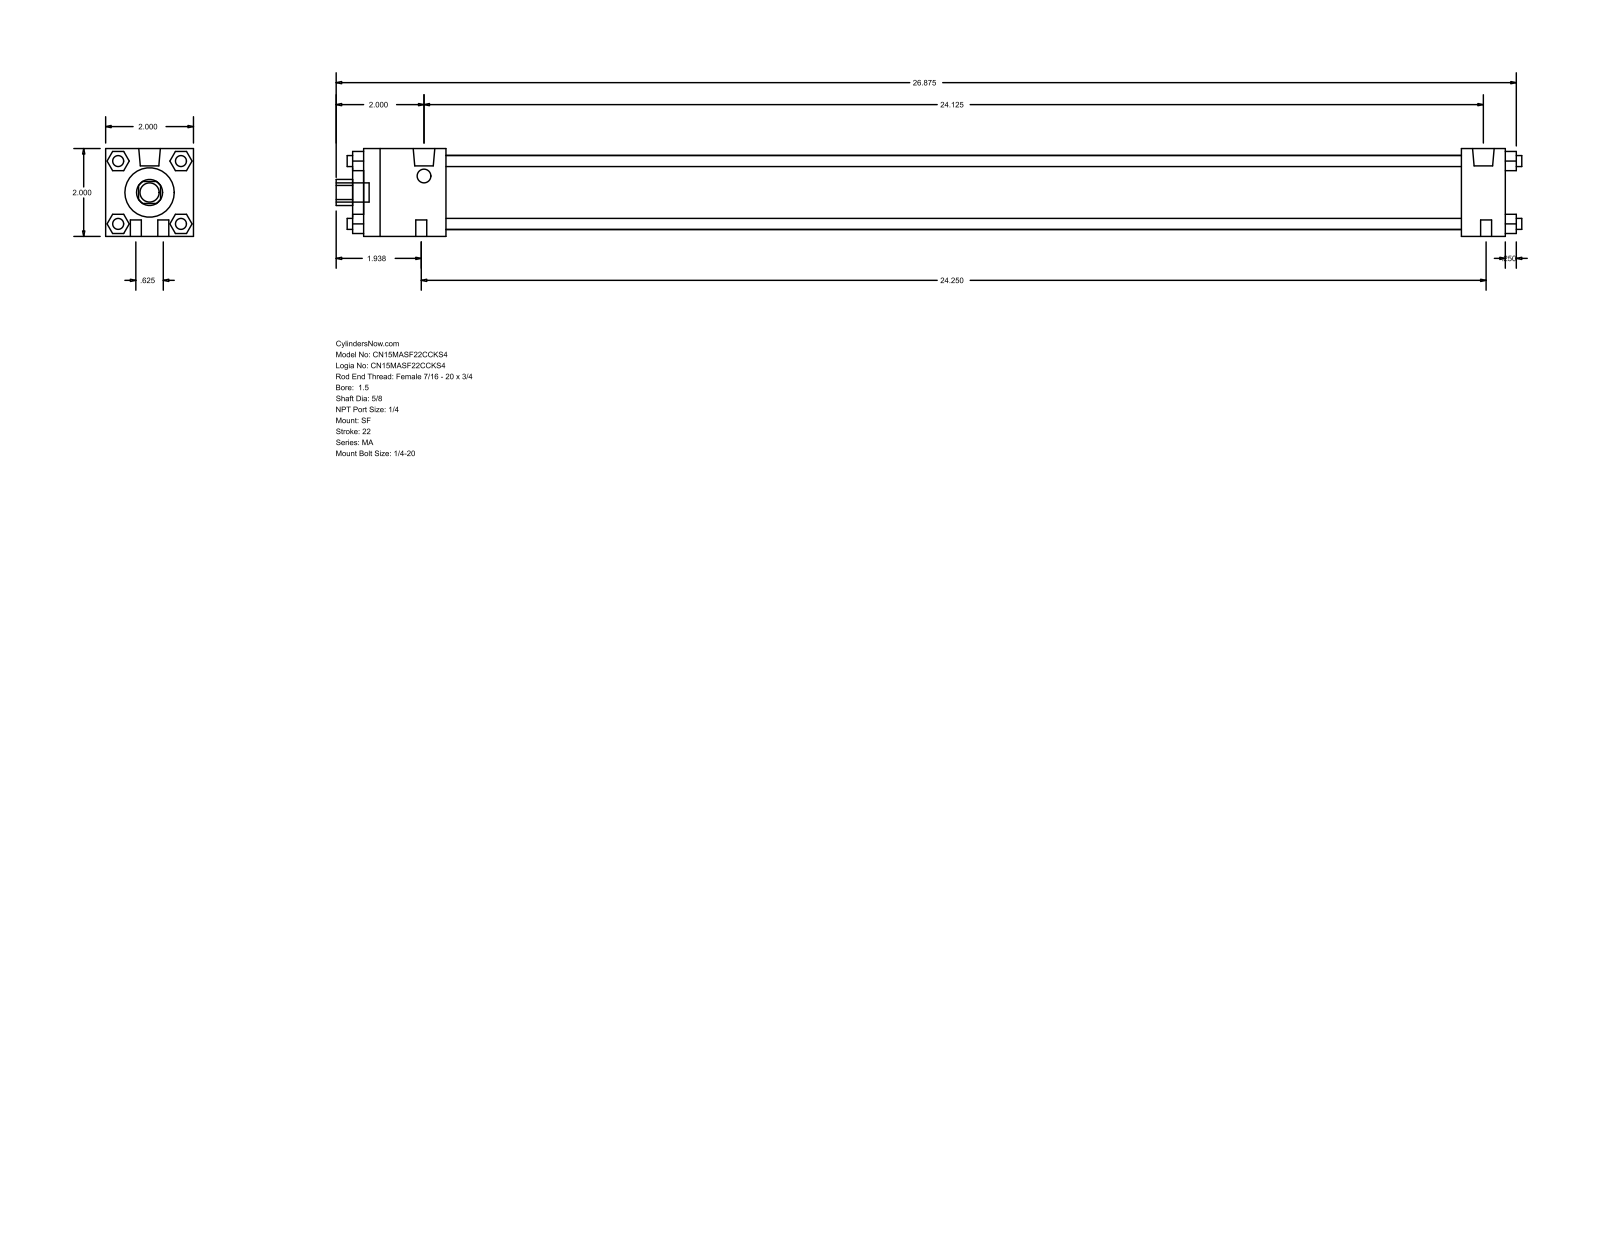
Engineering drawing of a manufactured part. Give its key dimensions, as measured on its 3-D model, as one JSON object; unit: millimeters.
{"part_name": "MA_SF__0150_0.625", "step_written_by": "GSSL Pune (CONFIG_CONTROL_DESIGN)", "units": "millimeters", "bodies": {"solids": 0, "faces": 124, "planar": 94, "cylindrical": 30, "other": 0}, "overall_size": [685.8, 50.8, 50.8], "round_holes": [[15.88, 1], [28.57, 1], [42.93, 1]], "round_bosses_or_shafts": [[6.35, 8], [12.49, 2], [7.94, 2], [11.11, 1]], "partial_cylinders_radius": [[7.54, 1]], "face_to_face_distances": [50.8, 660.39, 6.35, 666.74, 47.62, 635, 587.38, 612.77, 25.39, 53.97]}
